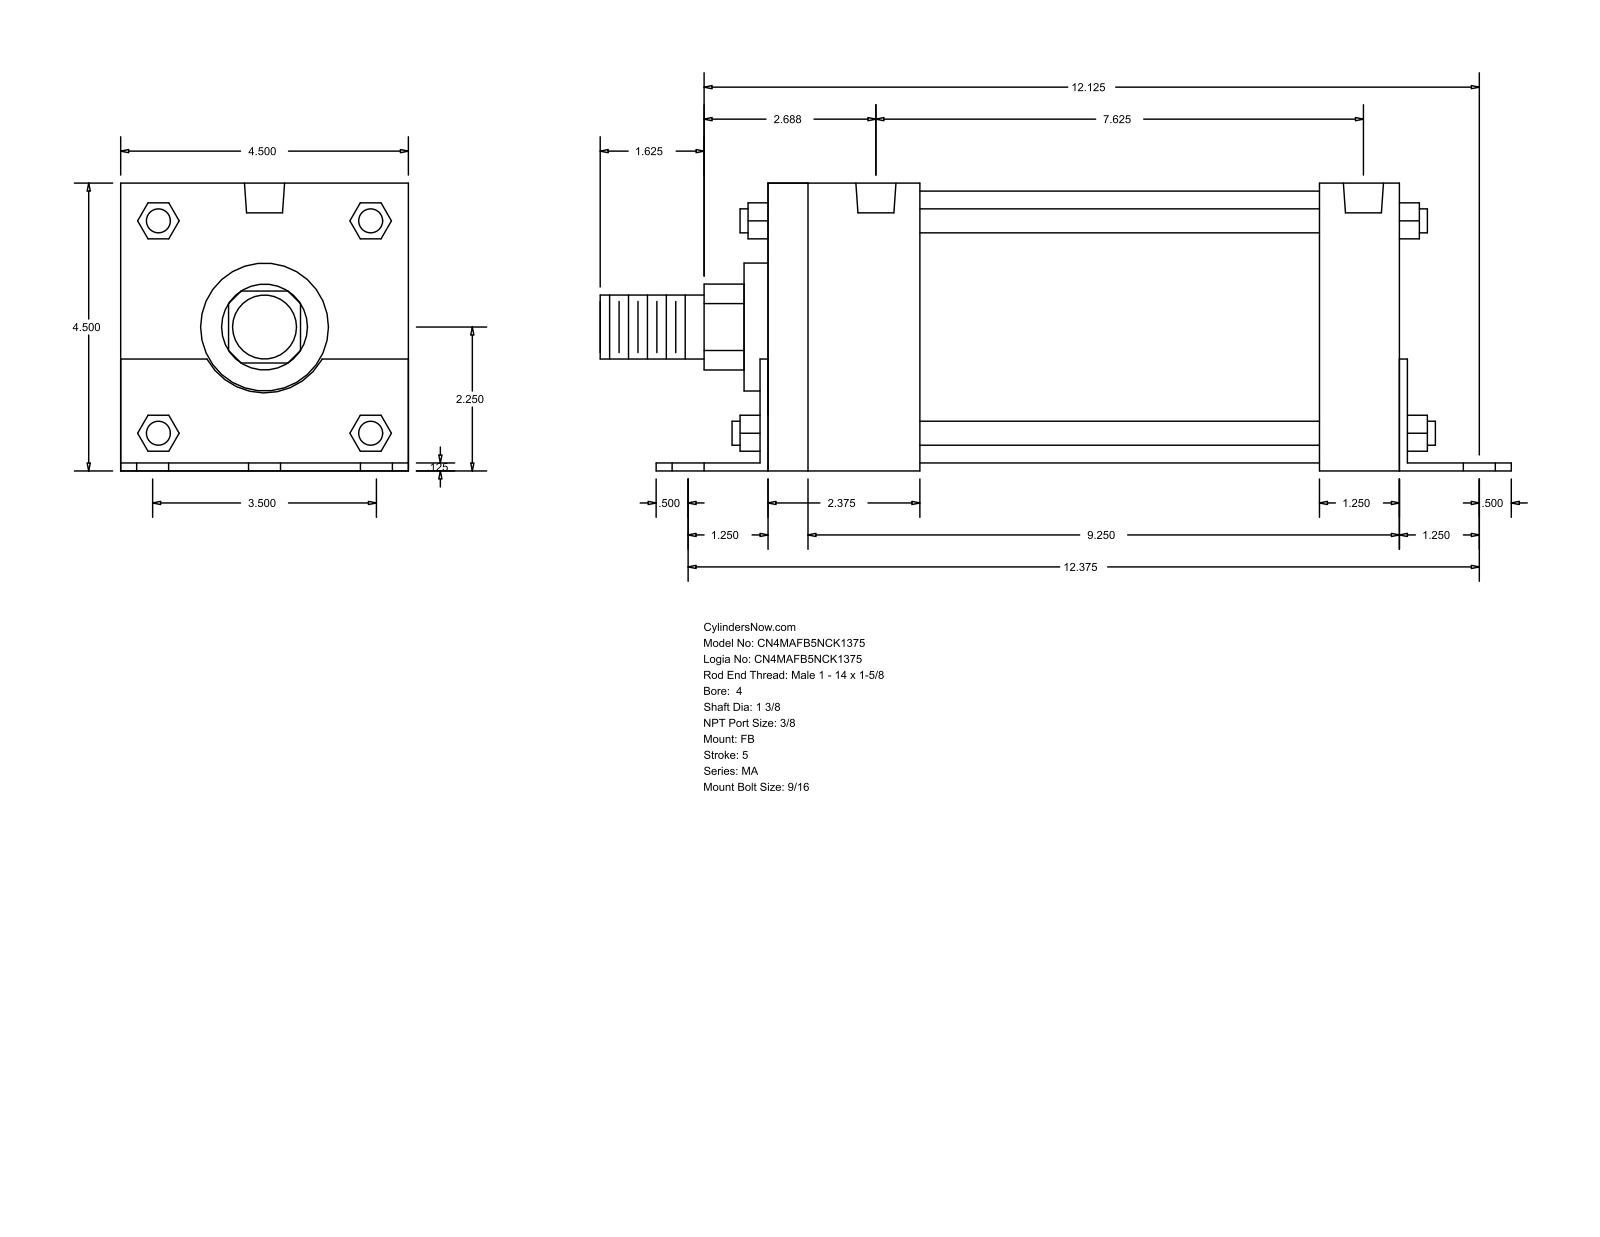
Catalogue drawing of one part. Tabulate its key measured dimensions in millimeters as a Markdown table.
| quantity | value |
| --- | --- |
| part name | MA_FB__0400_1.375 |
| STEP written by | GSSL Pune (CONFIG_CONTROL_DESIGN) |
| units | millimeters |
| bodies | 0 solids, 140 faces (105 planar, 35 cylindrical, 0 other) |
| overall size | 361.95 × 114.35 × 114.3 |
| round holes (diameter × count) | 14.29 × 6, 11.11 × 4, 15.93 × 2 |
| round bosses / shafts (diameter × count) | 9.53 × 4, 107.95 × 1, 50.8 × 1, 34.92 × 1, 25.4 × 1 |
| partial cylindrical surfaces (radius × count) | 17.06 × 1, 26.16 × 1 |
| main face-to-face distances | 114.3, 3.17, 114.35, 3.12, 111.18, 254, 250.83, 34.93, 257.17, 222.24 |
| hole center spacings | 44.45, 317.46, 314.33, 64, 67.5, 86.85, 88.9, 90.98 |
